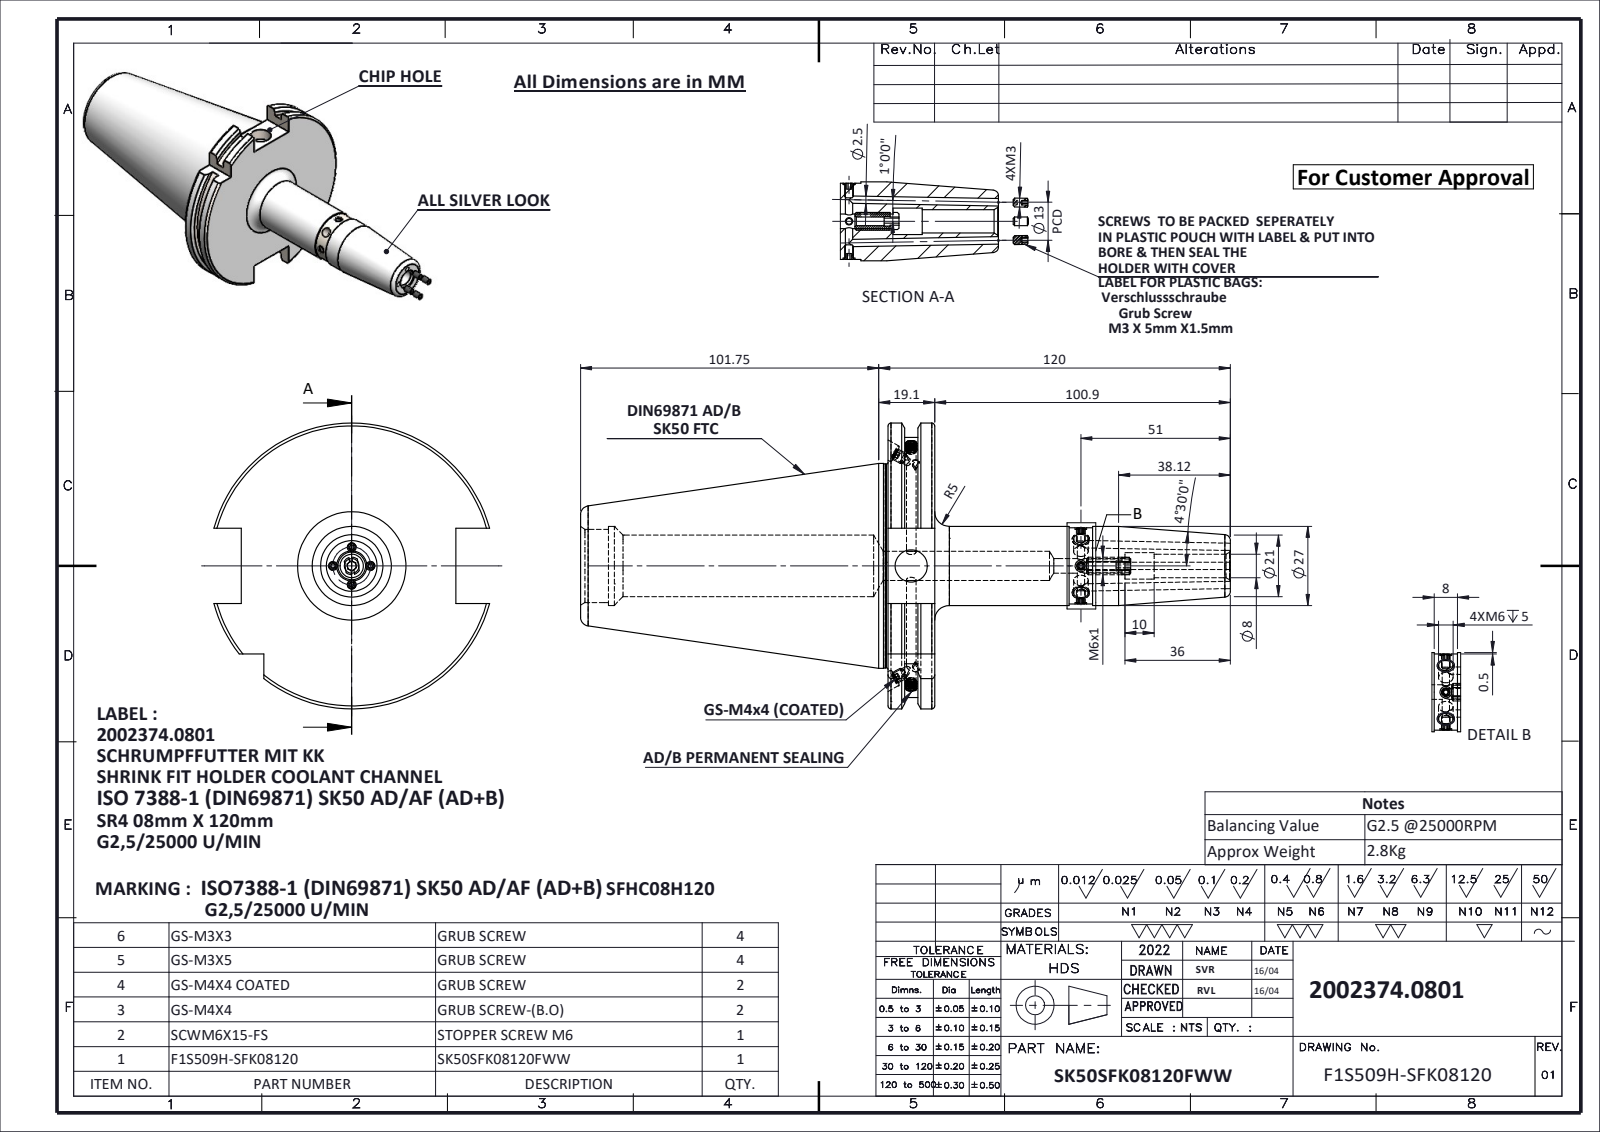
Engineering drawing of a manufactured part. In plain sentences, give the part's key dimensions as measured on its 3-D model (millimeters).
The part is named "GS-M3X5; GS-M4X4_DIN 913 - M4 x 4-N; SK50SFK08120FWW; socket set screw flat point_din_DIN 913 - M3 x 5-N (+3 more)". Its 3-D file was written by "SolidWorks 2024 (CONFIG_CONTROL_DESIGN)". It is 14 solids with 493 faces: 188 planar, 141 cylindrical and 164 other. Overall it measures 231.77 by 97.5 by 94.05 millimeters. Its volume is 369 815 cubic millimeters and its surface area 58 685 square millimeters. Round holes: 6 of diameter 2.5, 5 of diameter 5, 2 of diameter 3.2, 2 of diameter 4, 2 of diameter 6, 1 of diameter 3, 1 of diameter 3.3, 1 of diameter 8, 1 of diameter 9, 1 of diameter 10, 1 of diameter 11, 1 of diameter 21. Round bosses or shafts: 6 of diameter 3, 4 of diameter 4, 2 of diameter 2.9, 1 of diameter 69.85, 1 of diameter 69.45, 1 of diameter 27, 1 of diameter 26. Partial cylindrical surfaces (rounded edges, fillets, slot ends): 1 of radius 3, 1 of radius 44.9, 1 of radius 48.75. The main face-to-face distances are 15.9, 5.66, 10.24, 10.14, 4.48, 5.76, 104.95, 110.61, 115.09, 120.85. The hole center spacings are 57.9.
